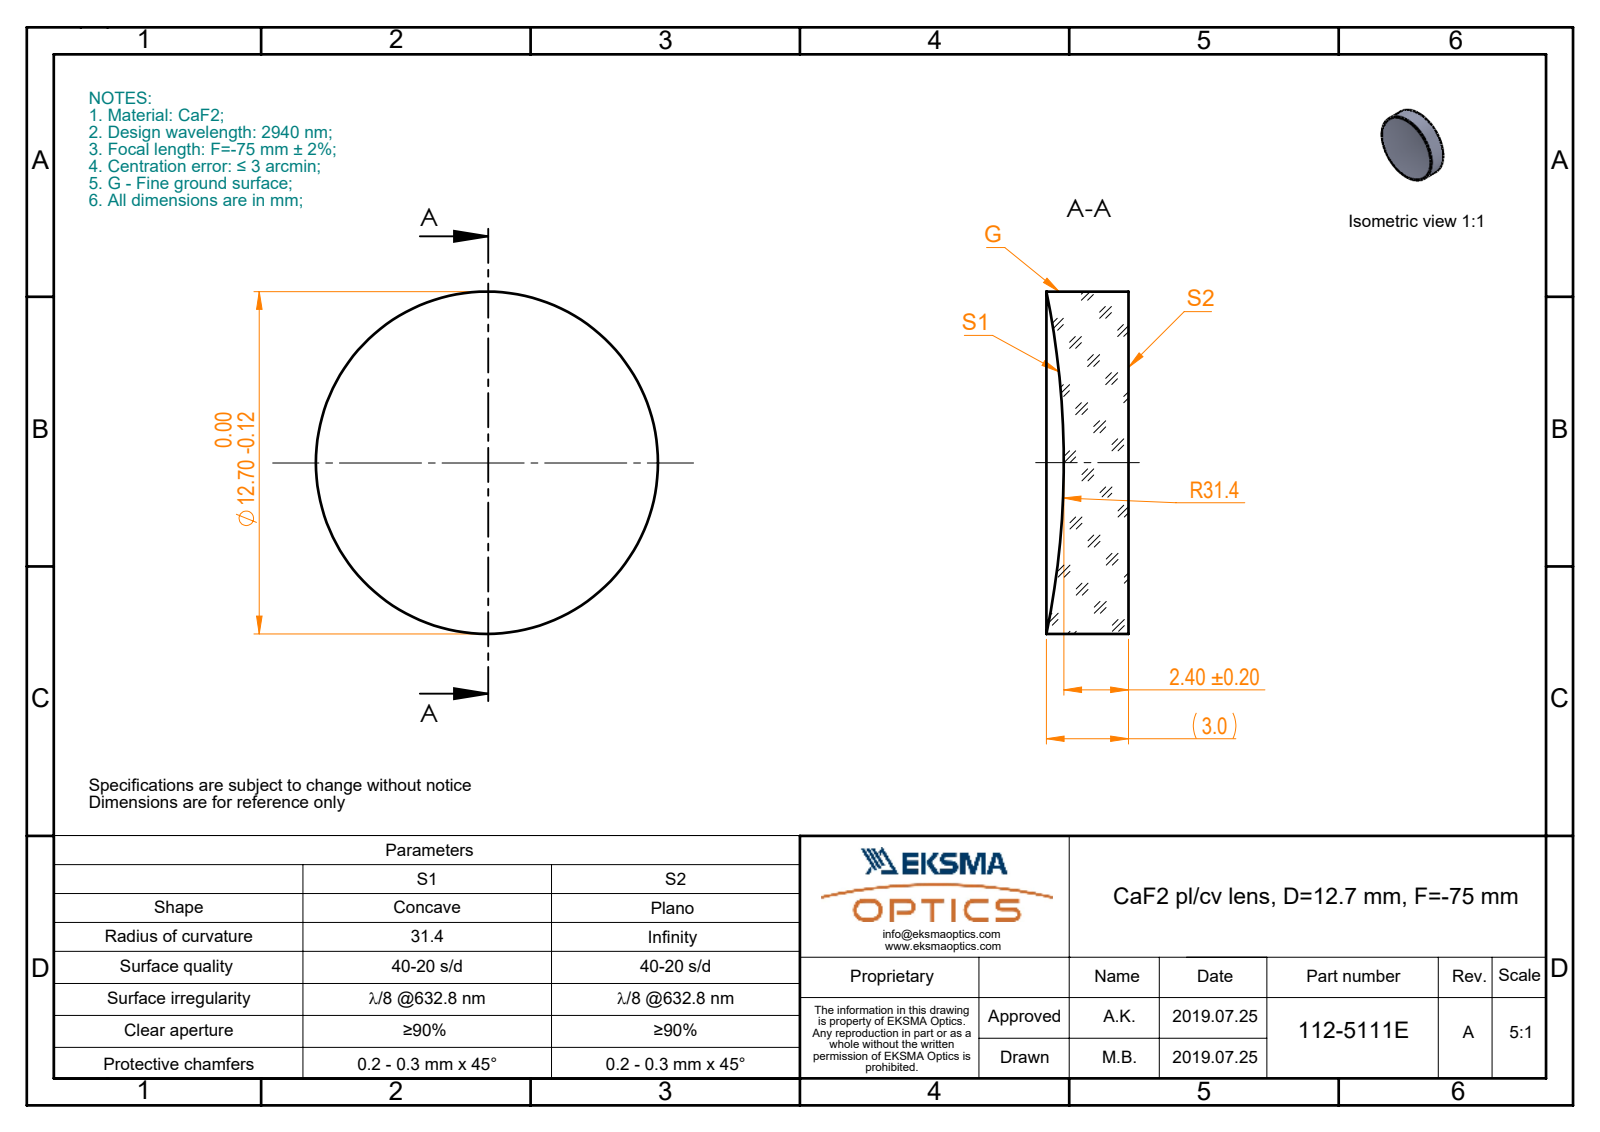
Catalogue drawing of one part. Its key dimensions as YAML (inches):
part_name: "112-5111E CaF2 pl-cv 12.7 F-75"
step_written_by: "SolidWorks 2017 (CONFIG_CONTROL_DESIGN)"
units: inches
bodies: {solids: 1, faces: 5, planar: 1, cylindrical: 2, other: 2}
overall_size: [0.5, 0.5, 0.12]
volume: 0.021
surface_area: 0.583
round_bosses_or_shafts:
  - {diameter: 0.5, count: 1}
